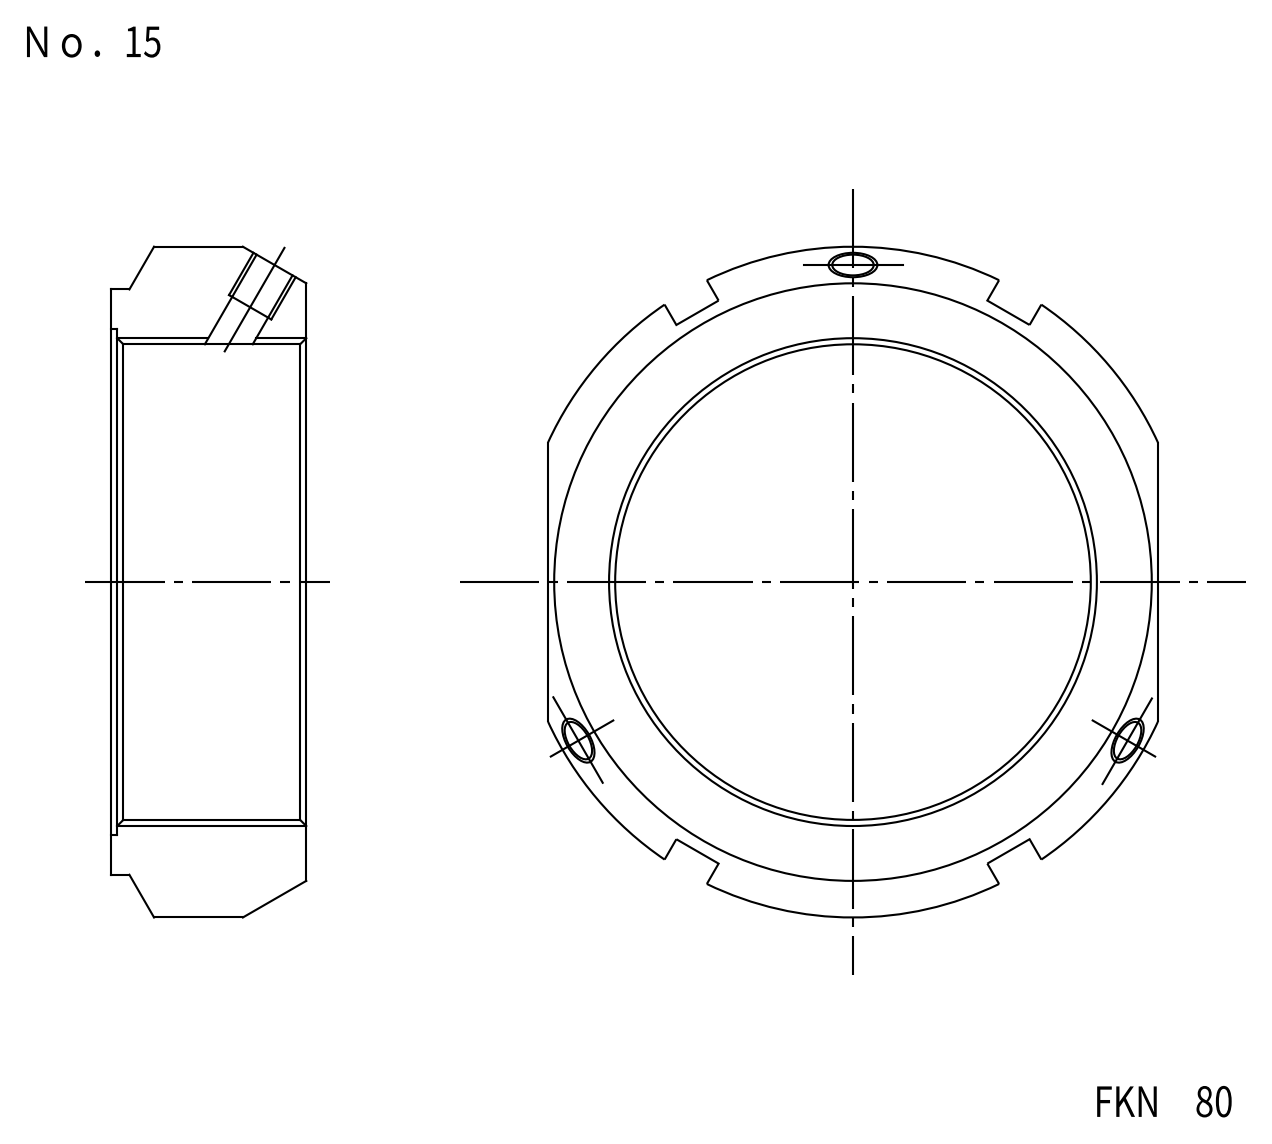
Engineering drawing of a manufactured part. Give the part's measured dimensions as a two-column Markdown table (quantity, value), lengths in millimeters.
| quantity | value |
| --- | --- |
| part name | FKD FKN80 |
| STEP written by | Autodesk Inventor LT (CONFIG_CONTROL_DESIGN) |
| units | millimeters |
| bodies | 1 solid, 40 faces (20 planar, 18 cylindrical, 2 other) |
| overall size | 110 × 100 × 32 |
| volume | 111 120 mm³ |
| surface area | 26 029 mm² |
| round holes (diameter × count) | 6.65 × 3, 8.1 × 3, 80 × 1, 83 × 1 |
| round bosses / shafts (diameter × count) | 96 × 1 |
| partial cylindrical surfaces (radius × count) | 55 × 1 |
| main face-to-face distances | 32, 100, 1.5, 30.5, 102, 8 |
